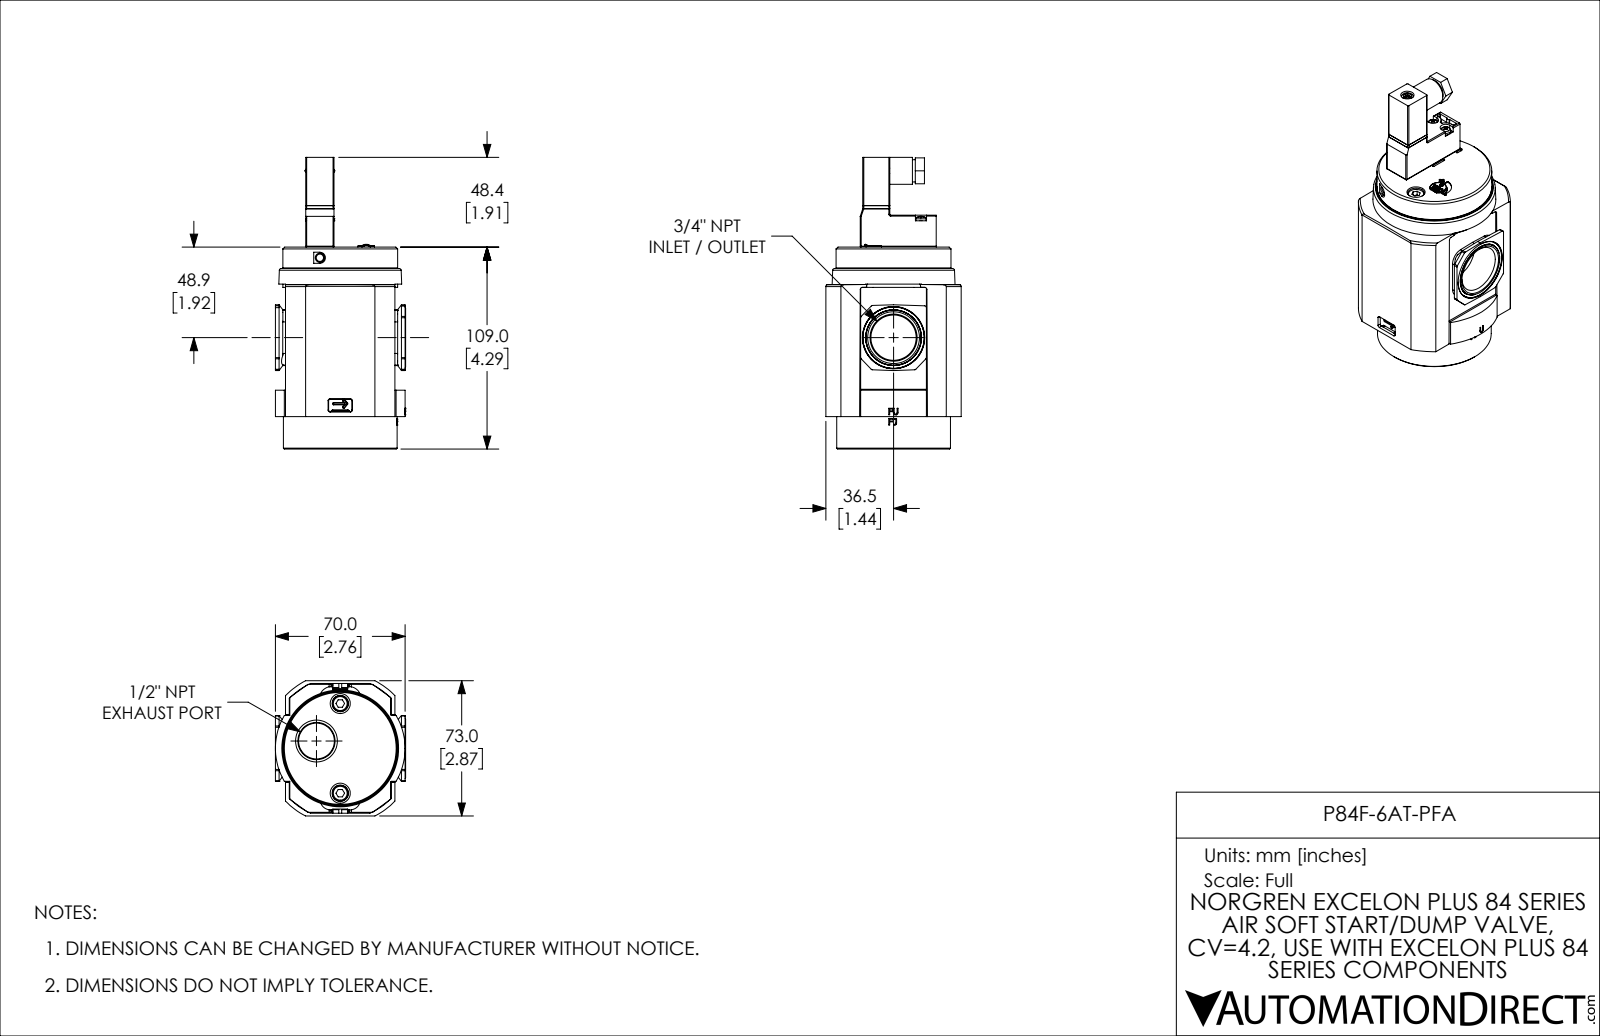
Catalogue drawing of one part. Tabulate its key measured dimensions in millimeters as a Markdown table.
| quantity | value |
| --- | --- |
| part name | P84F-6AT-PFA |
| STEP written by | SolidWorks 2021 (CONFIG_CONTROL_DESIGN) |
| units | millimeters |
| bodies | 8 solids, 1169 faces (576 planar, 354 cylindrical, 239 other) |
| overall size | 157.35 × 73 × 70.25 |
| volume | 409 080 mm³ |
| surface area | 98 039 mm² |
| round holes (diameter × count) | 4.92 × 4, 5.3 × 4, 8.8 × 4, 1.5 × 3, 2.46 × 3, 0.8 × 2, 1.9 × 2, 3.1 × 2, 8.5 × 2, 1.78 × 1, 3 × 1, 3.8 × 1 |
| round bosses / shafts (diameter × count) | 8.5 × 4, 5 × 4, 3 × 2, 62 × 1, 61.4 × 1, 59 × 1, 14.5 × 1, 12 × 1 |
| partial cylindrical surfaces (radius × count) | 0.5 × 34, 0.25 × 14, 1 × 13, 3 × 4, 6 × 4, 6.3 × 4, 0.26 × 3, 0.34 × 3 |
| main face-to-face distances | 1.5, 70.2, 2, 71, 71.5, 0.5, 69.5, 11.25, 70, 81.45 |
| hole center spacings | 3.8, 5.05, 5.41, 7.11, 12.41, 21.05, 24.88, 46.75 |
